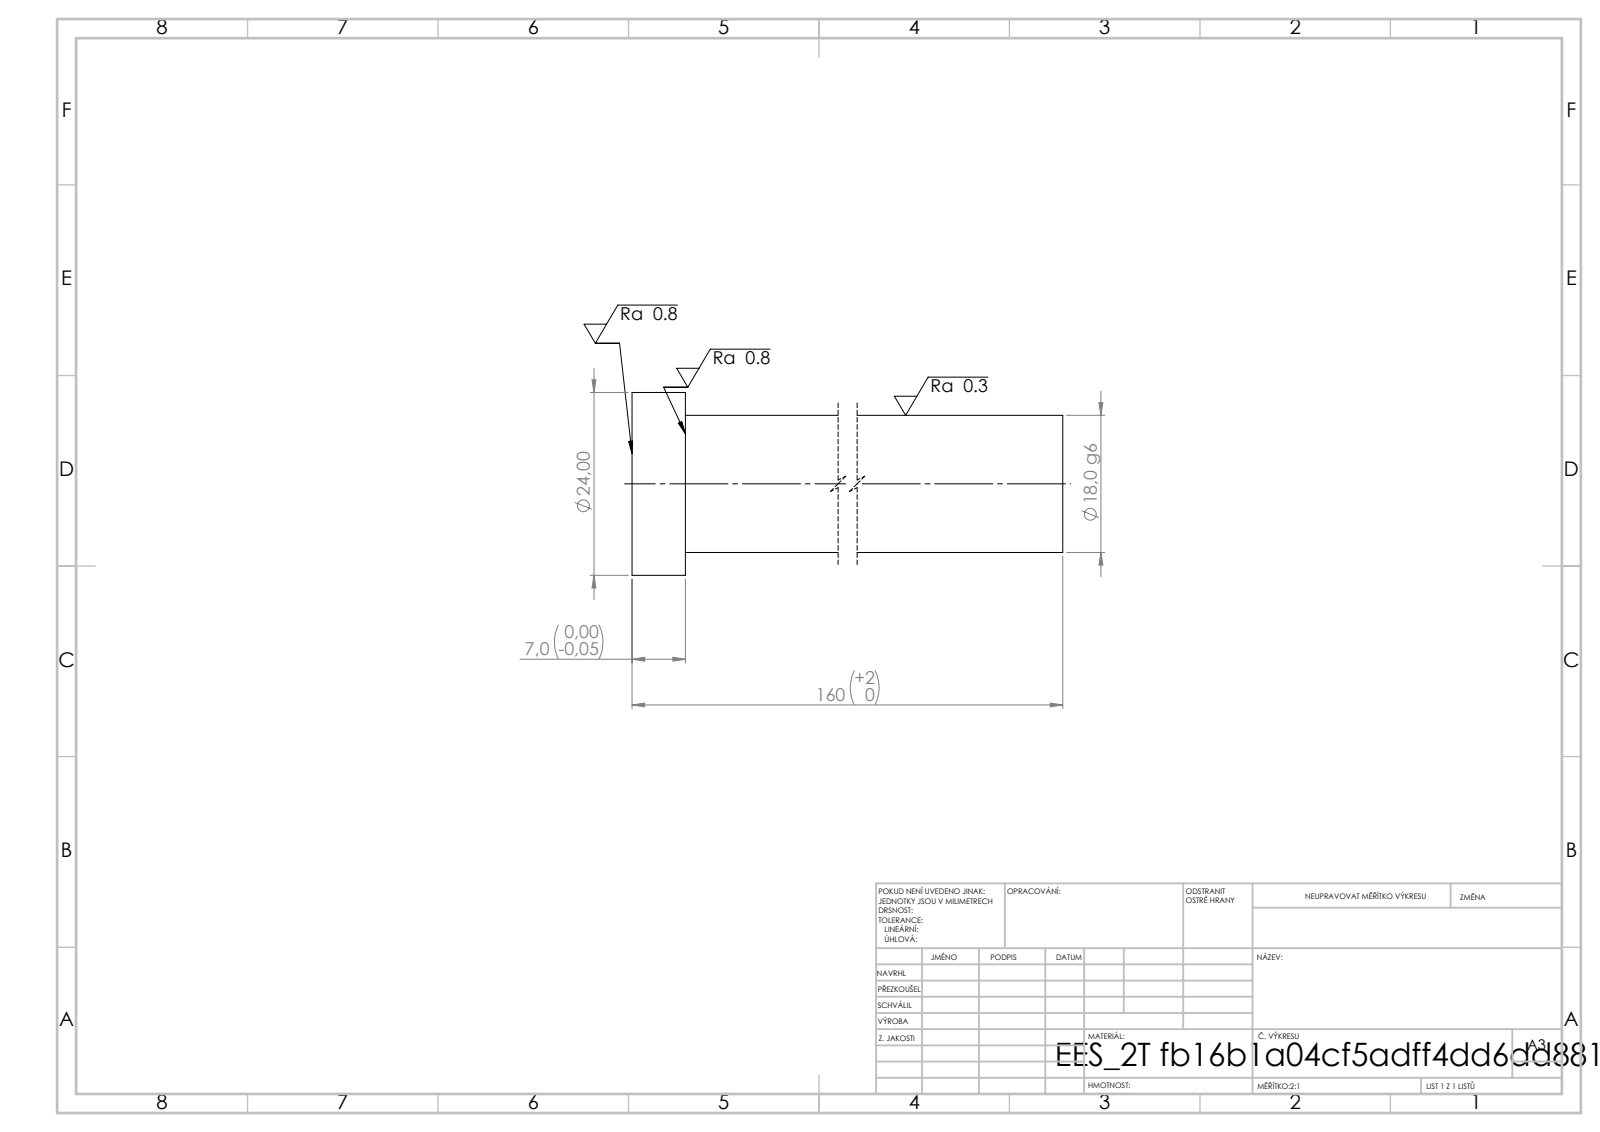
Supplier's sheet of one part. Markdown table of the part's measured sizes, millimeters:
| quantity | value |
| --- | --- |
| STEP written by | SolidWorks 2019 (CONFIG_CONTROL_DESIGN) |
| units | millimeters |
| bodies | 1 solid, 7 faces (3 planar, 4 cylindrical, 0 other) |
| overall size | 160 × 24 × 24 |
| volume | 42 100 mm³ |
| surface area | 10 085 mm² |
| round bosses / shafts (diameter × count) | 24 × 1, 18 × 1 |
| main face-to-face distances | 160, 7, 153 |
